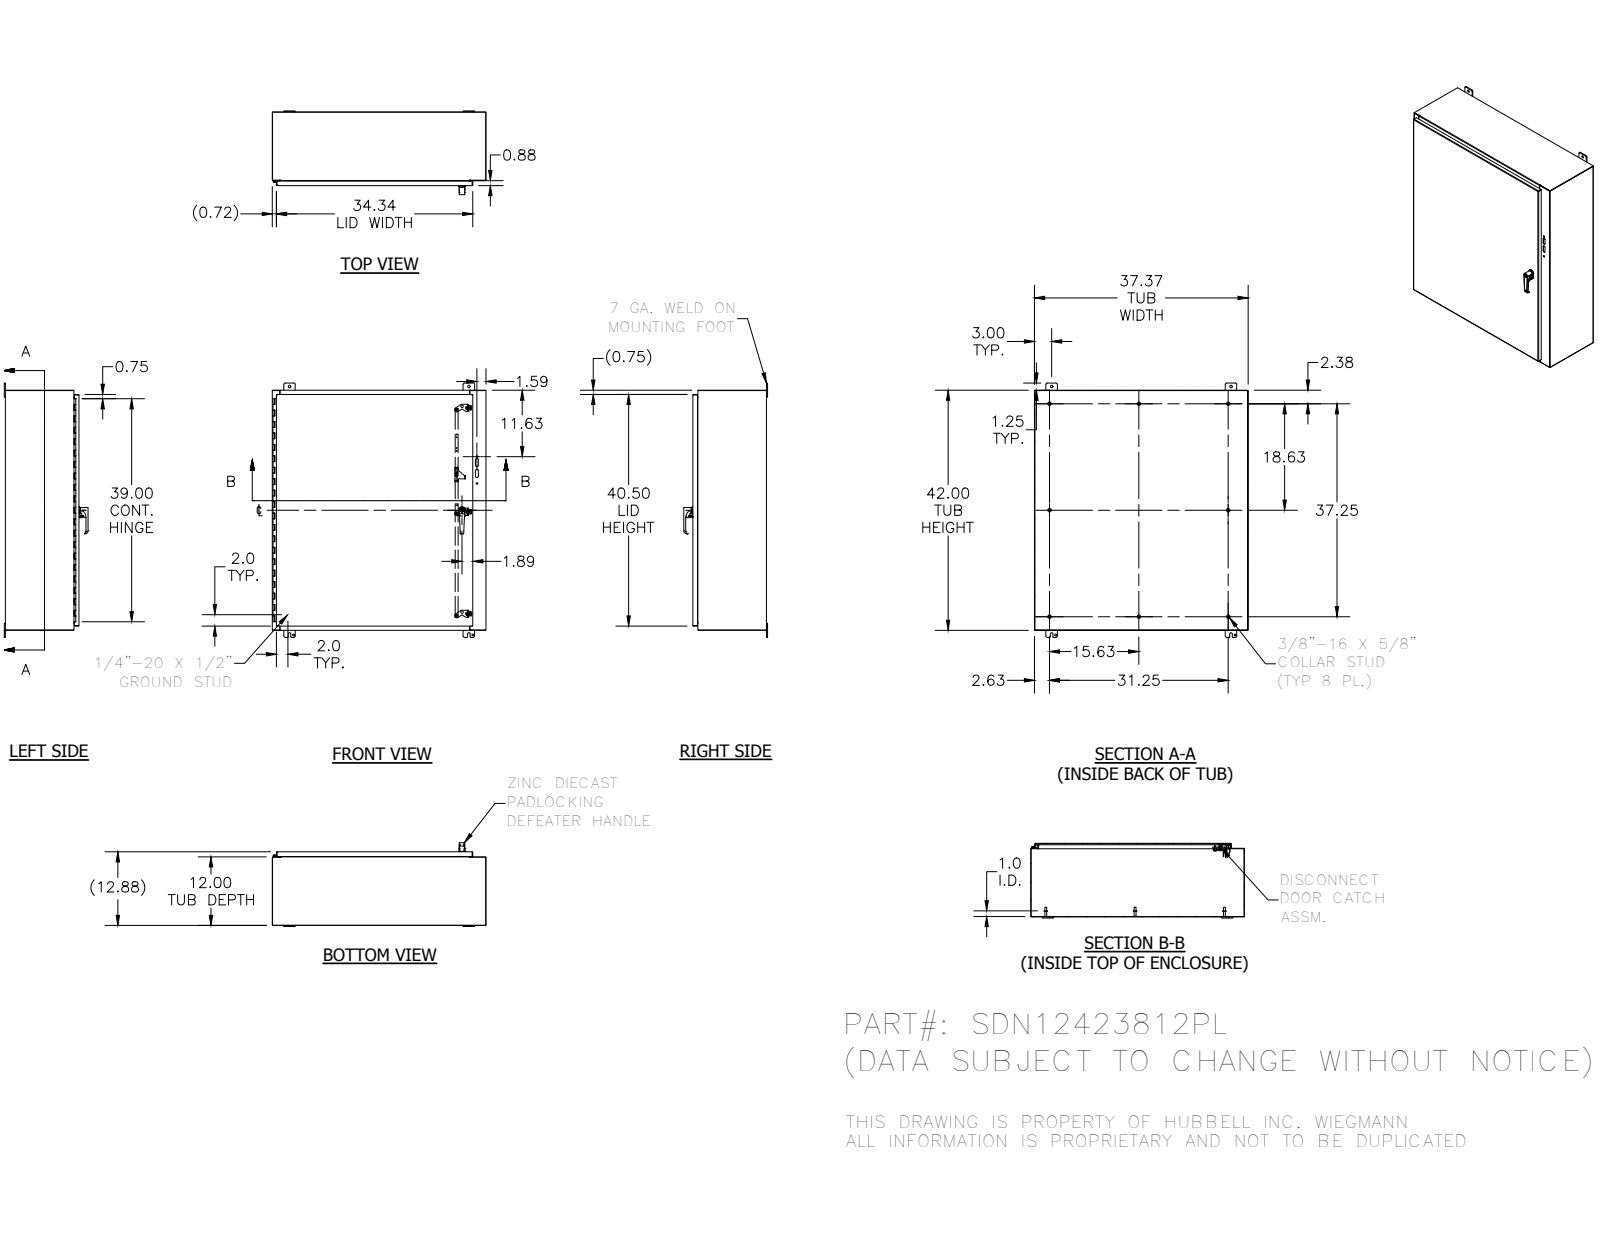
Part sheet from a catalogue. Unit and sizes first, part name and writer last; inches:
Units: inches
Overall size (bounding box): 44.5 × 37.375 × 14.649
Round holes (diameter × count): ⌀0.145 ×6, ⌀0.313 ×4, ⌀0.32 ×4, ⌀0.438 ×4, ⌀0.196 ×3, ⌀0.211 ×3, ⌀0.22 ×3, ⌀0.313 ×3, ⌀0.45 ×3, ⌀0.156 ×2, ⌀0.281 ×2, ⌀0.307 ×2
Round bosses / shafts (diameter × count): ⌀0.625 ×10, ⌀0.33 ×10, ⌀0.437 ×6, ⌀0.3 ×6, ⌀0.225 ×6, ⌀0.25 ×4, ⌀0.19 ×4, ⌀0.75 ×3
Partial cylindrical surfaces — rounded edges, fillets, slot ends (radius × count): R0.02 ×38, R0.012 ×30, R0.025 ×24, R0.25 ×23, R0.125 ×21, R0.031 ×18, R0.105 ×18, R0.094 ×6
Main face-to-face distances: 0.074, 12.801, 12.727, 12.875, 37.301, 41.926, 37.227, 37.375, 11.926, 0.875
Hole centre spacings: 36, 17.844, 18.156, 1.593, 31.375, 42, 52.425, 0.5
Volume: 412.7 in³ · Surface area: 11 073 in²
Bodies: 64 solids, 1801 faces (957 planar, 588 cylindrical, 256 other)
Part name (STEP PRODUCT): SDN12423812PL; SDN12423812PLBLR; 3889; 34840 (+8 more)
STEP written by: Autodesk Inventor 2012 (AUTOMOTIVE_DESIGN)
